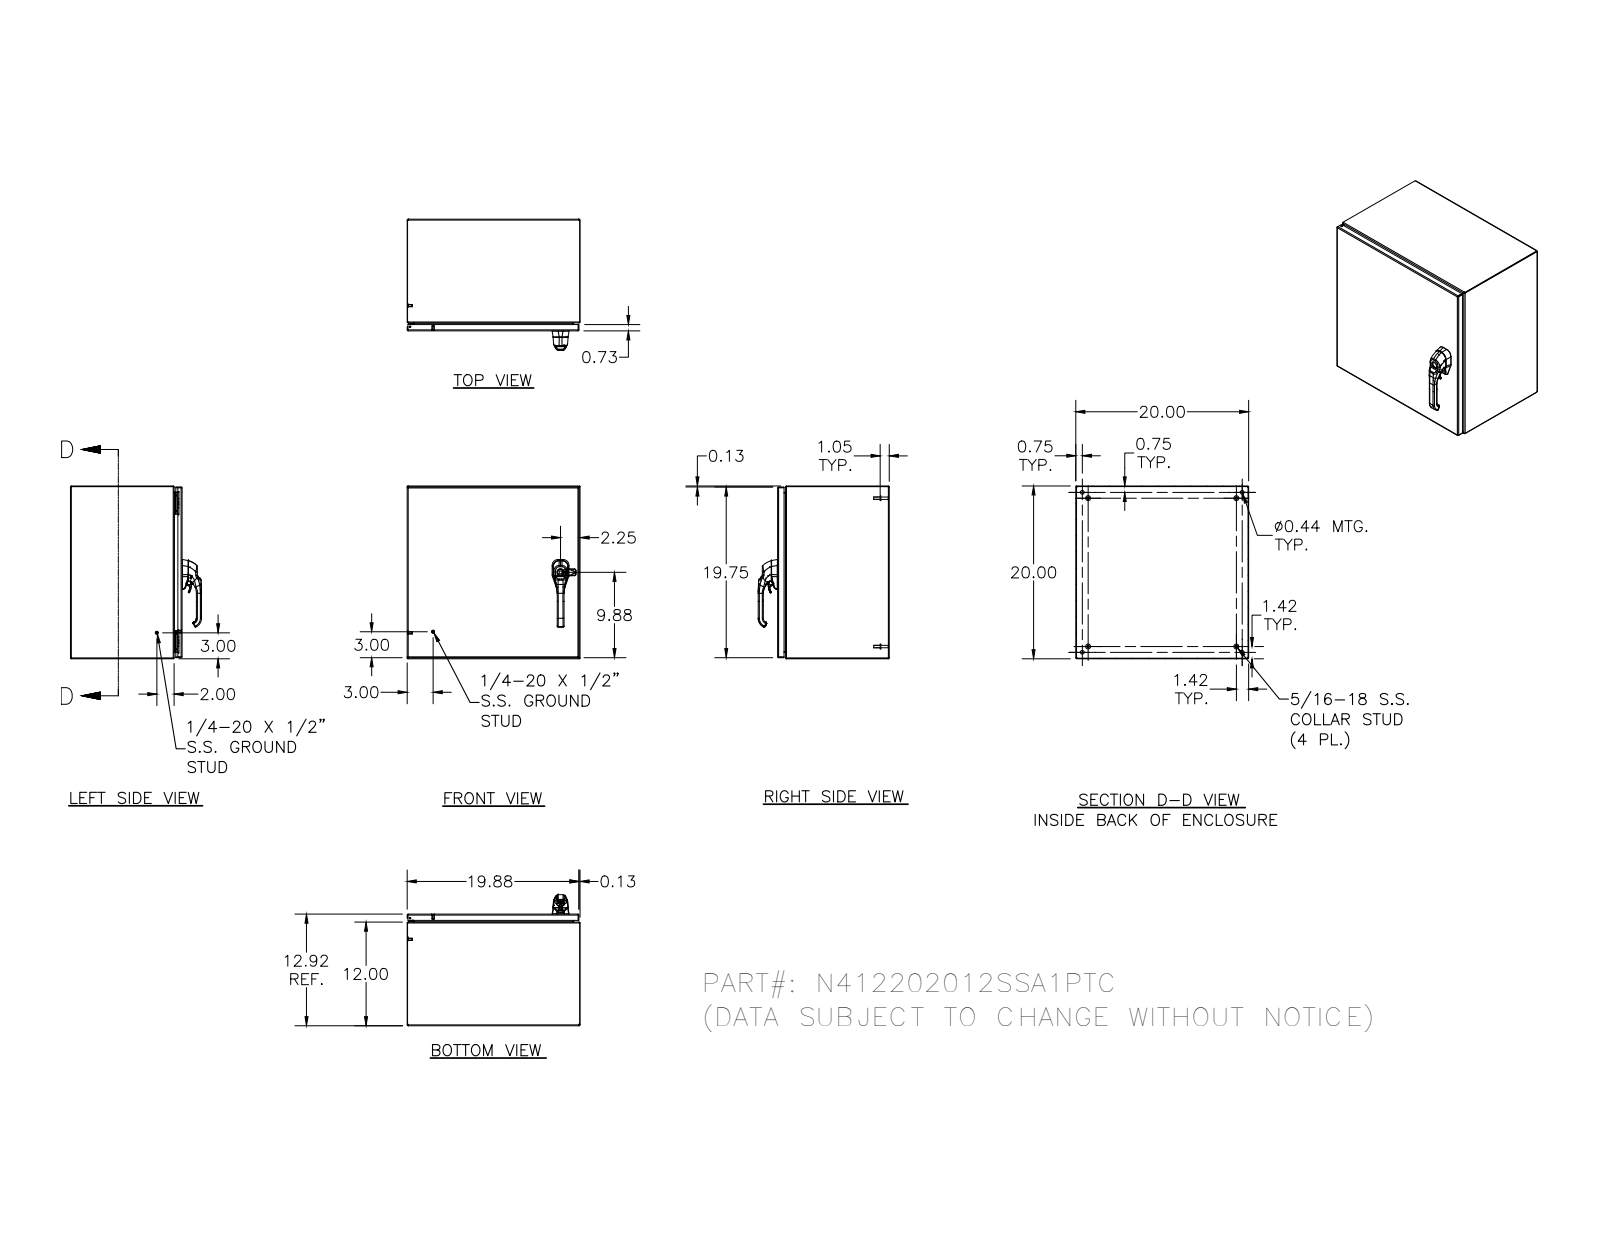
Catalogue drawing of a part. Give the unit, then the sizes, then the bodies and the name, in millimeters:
Units: millimetres
Overall size (bounding box): 508 × 508 × 385.2
Round holes (diameter × count): ⌀4.8 ×5, ⌀2.4 ×4, ⌀3.9 ×4, ⌀4.2 ×4, ⌀4.4 ×4, ⌀11.1 ×4, ⌀5.4 ×3, ⌀7.1 ×3, ⌀4 ×2, ⌀8 ×2, ⌀10.2 ×2, ⌀10.5 ×2
Round bosses / shafts (diameter × count): ⌀6.4 ×10, ⌀14.3 ×4, ⌀9.1 ×4, ⌀8.1 ×4, ⌀7.6 ×4, ⌀7 ×4, ⌀6.5 ×4, ⌀4.2 ×4
Partial cylindrical surfaces — rounded edges, fillets, slot ends (radius × count): R0.5 ×174, R0.3 ×101, R0.8 ×30, R1.3 ×26, R0.5 ×21, R2.7 ×20, R0.4 ×18, R2 ×14
Main face-to-face distances: 1.9, 506.1, 326.2, 504.2, 508, 328.1, 324.3, 302.9, 23.3, 18.8
Hole centre spacings: 406.3, 469.9, 479.3, 0.4, 16.8, 406.5, 423.1, 0.5
Volume: 2 443 000 mm³ · Surface area: 2 550 000 mm²
Bodies: 41 solids, 2784 faces (882 planar, 1037 cylindrical, 865 other)
Part name (STEP PRODUCT): N412202012SSA1PTC; N412202012SSA1PTCBKP; N4122020SSA1PTCLID; HFW328176 (+8 more)
STEP written by: Autodesk Inventor 2012 (AUTOMOTIVE_DESIGN)
